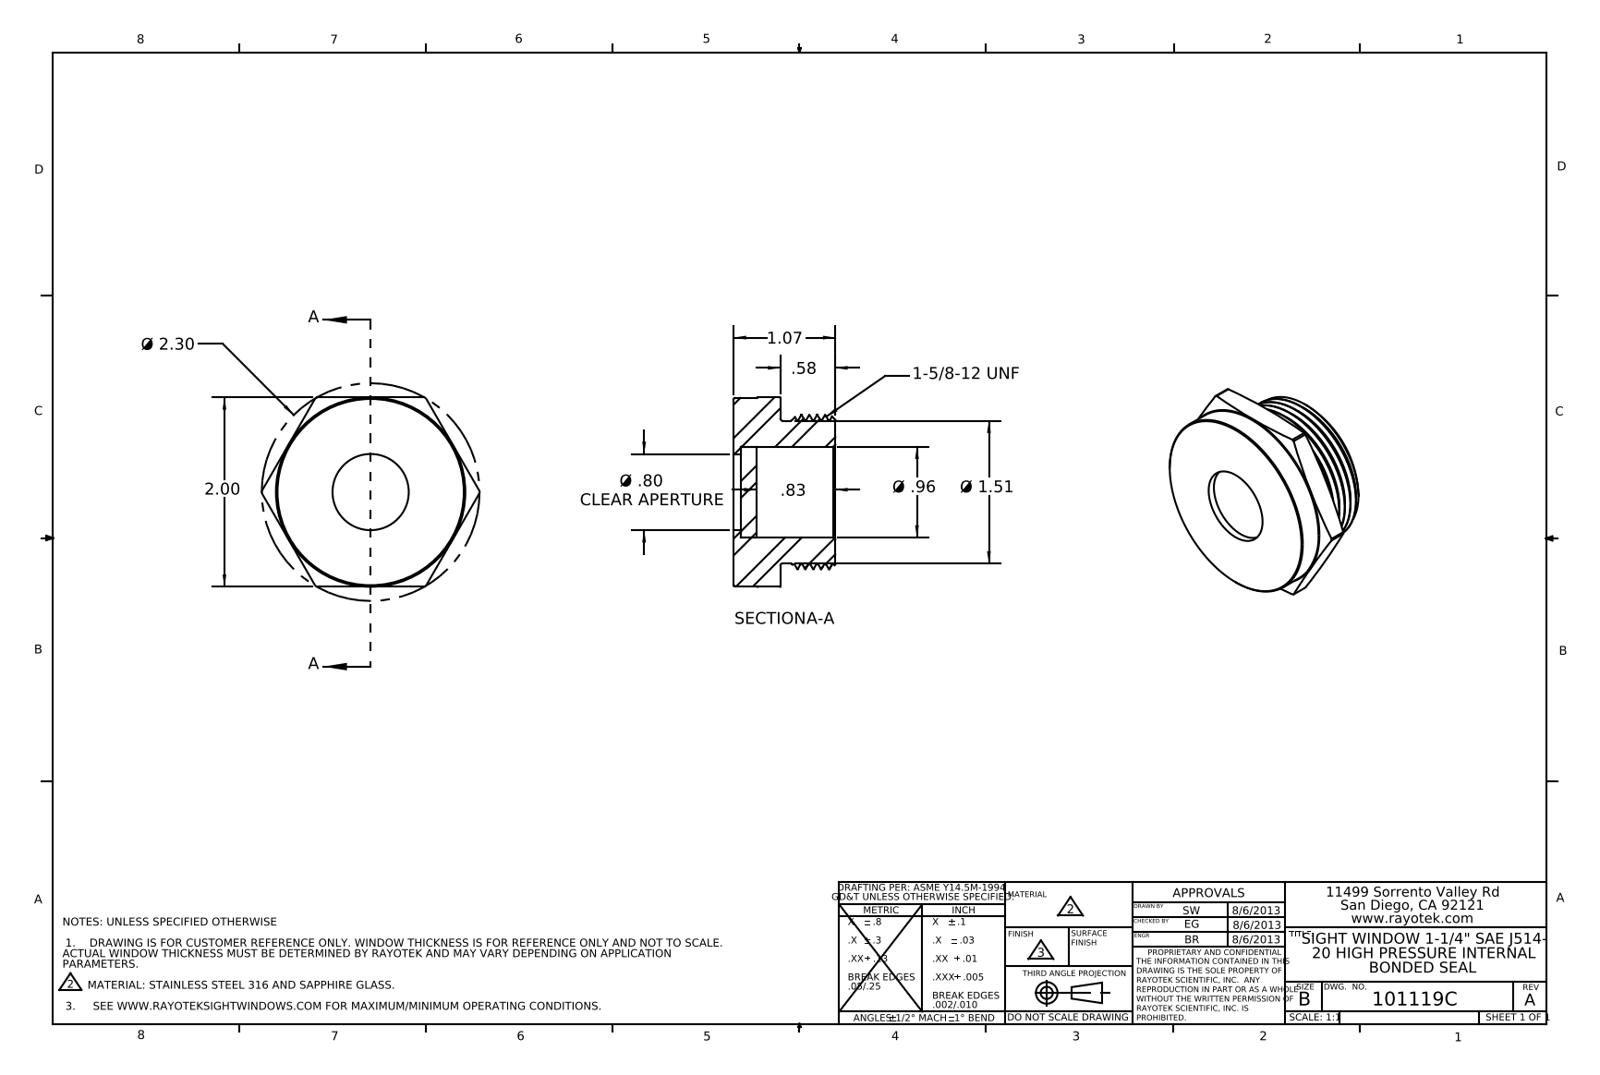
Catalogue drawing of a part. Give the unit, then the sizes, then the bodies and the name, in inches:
Units: inches
Overall size (bounding box): 2.297 × 2 × 1.07
Round holes (diameter × count): ⌀0.804 ×1, ⌀0.96 ×1
Round bosses / shafts (diameter × count): ⌀1.985 ×1, ⌀1.625 ×1, ⌀1.507 ×1
Partial cylindrical surfaces — rounded edges, fillets, slot ends (radius × count): R1.149 ×1
Main face-to-face distances: 0.49, 0.58, 1.07, 0.992, 0.412, 0.078, 2, 0.832, 0.252, 0.16
Volume: 2.052 in³ · Surface area: 18.29 in²
Bodies: 2 solids, 61 faces (12 planar, 26 cylindrical, 23 other)
Part name (STEP PRODUCT): 403119
STEP written by: SolidWorks 2012 (AUTOMOTIVE_DESIGN)
